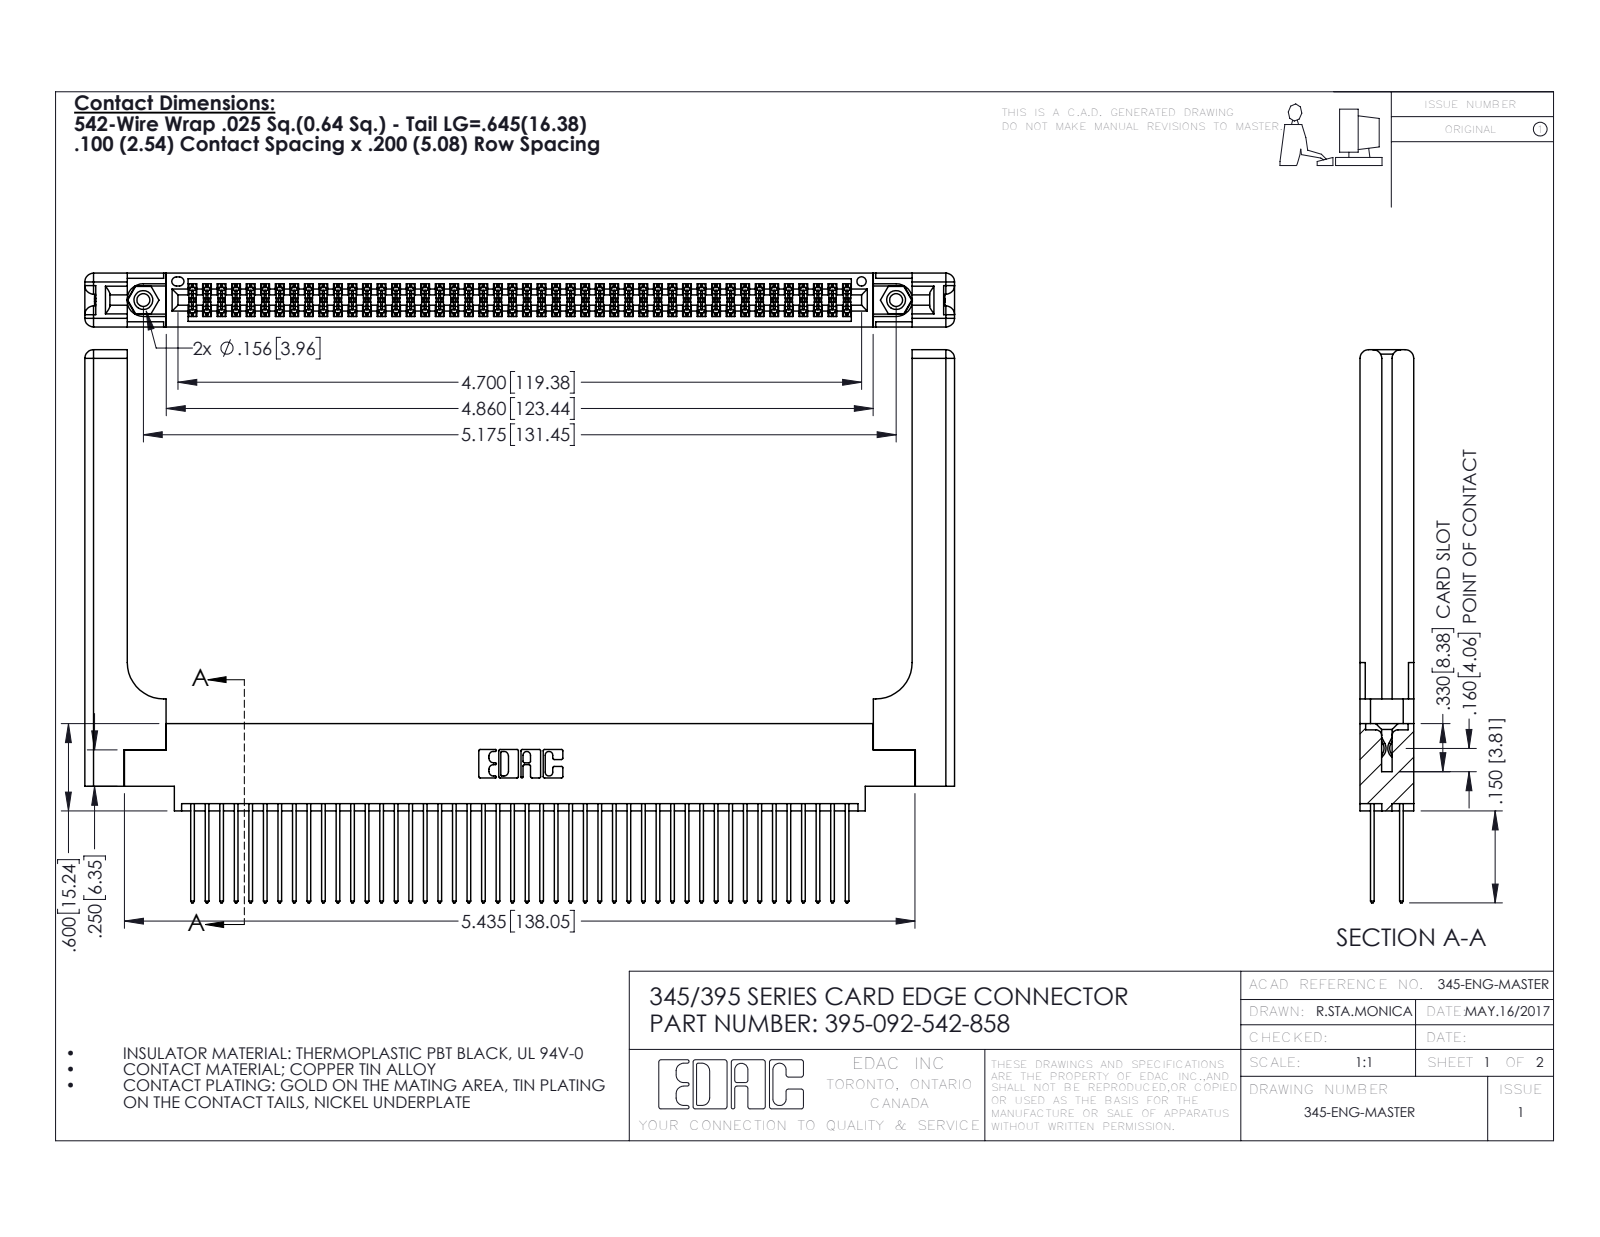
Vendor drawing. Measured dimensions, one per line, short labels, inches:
name: 345 Part_0.170 Offset - 0.156 Dia-TH; 395-092-542-858; 345-292-001_345-293-142; 345-250-001_345-250-001-102 (+1 more)
written by: SolidWorks 2016 (CONFIG_CONTROL_DESIGN)
unit: in
bodies: 97 solids, 4986 faces (3268 planar, 1658 cylindrical, 60 other)
size: 5.979 × 3.802 × 0.37
volume: 1.439 in³; area: 45.9 in²
holes: 2× ⌀0.089, 2× ⌀0.125, 2× ⌀0.156, 1× ⌀0.064
bosses: 2× ⌀0.155
rounds: 138× R0.006, 92× R0.01, 22× R0.01, 16× R0.06, 6× R0.007, 6× R0.031, 3× R0.026, 2× R0.014
face distances: 0.072, 0.298, 0.37, 0.098, 0.272, 0.025, 0.2, 0.225, 0.175, 0.148
hole spacings: 0.27, 4.939, 5.175
